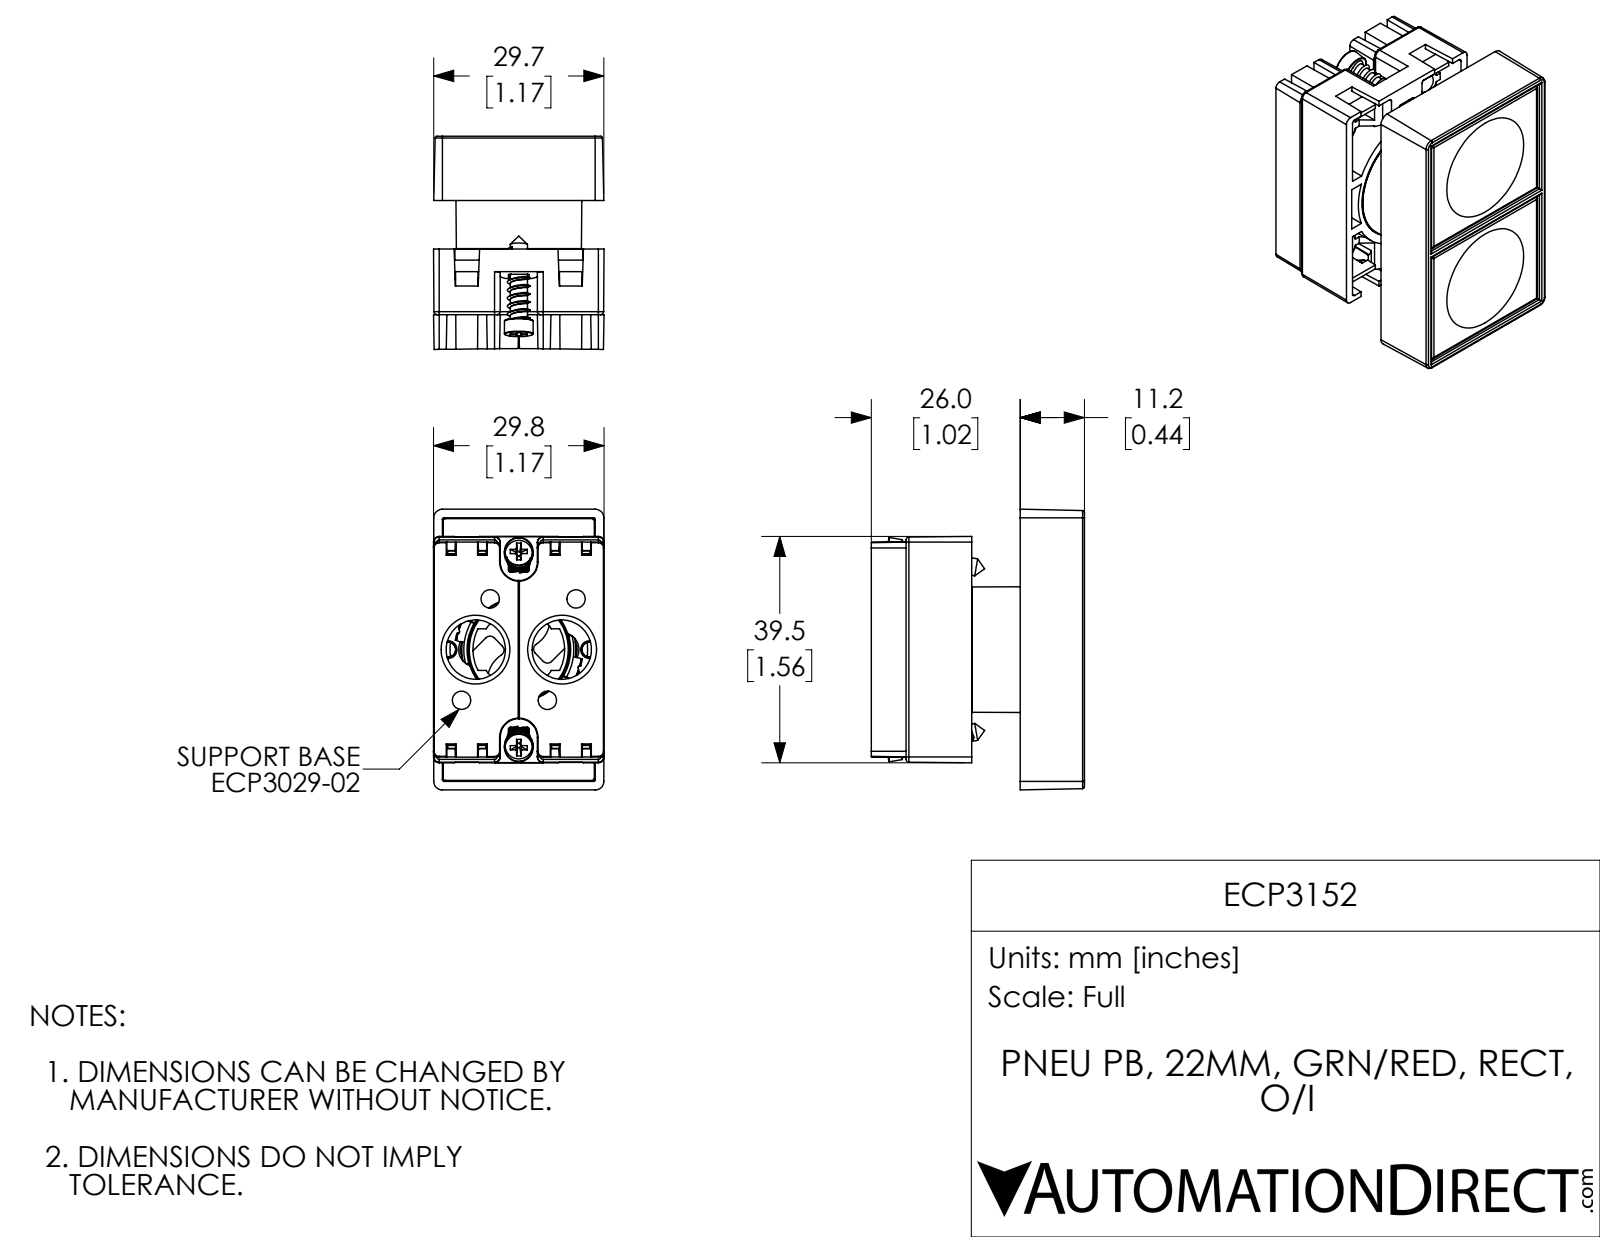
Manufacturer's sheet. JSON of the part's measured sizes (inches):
{"part_name": "ECP3152", "step_written_by": "SolidWorks 2017 (AUTOMOTIVE_DESIGN)", "units": "inches", "bodies": {"solids": 8, "faces": 877, "planar": 401, "cylindrical": 181, "other": 295}, "overall_size": [1.929, 1.465, 1.173], "volume_in3": 1.099, "surface_area_in2": 36.92, "round_holes": [[0.081, 4], [0.315, 2], [0.407, 2], [0.697, 1], [0.756, 1]], "round_bosses_or_shafts": [[0.374, 2], [0.197, 2], [0.118, 2], [0.866, 1]], "partial_cylinders_radius": [[0.012, 30], [0.02, 24], [0.039, 12], [0.006, 8], [0.008, 4], [0.008, 2], [0.118, 2], [0.128, 2]], "face_to_face_distances": [0.059, 1.135, 0.232, 0.903, 0.291, 0.844, 0.067, 0.079, 0.37, 0.311], "hole_center_spacings": [0.304, 0.366, 0.487, 0.541, 0.665, 0.817, 0.217, 0.295]}
